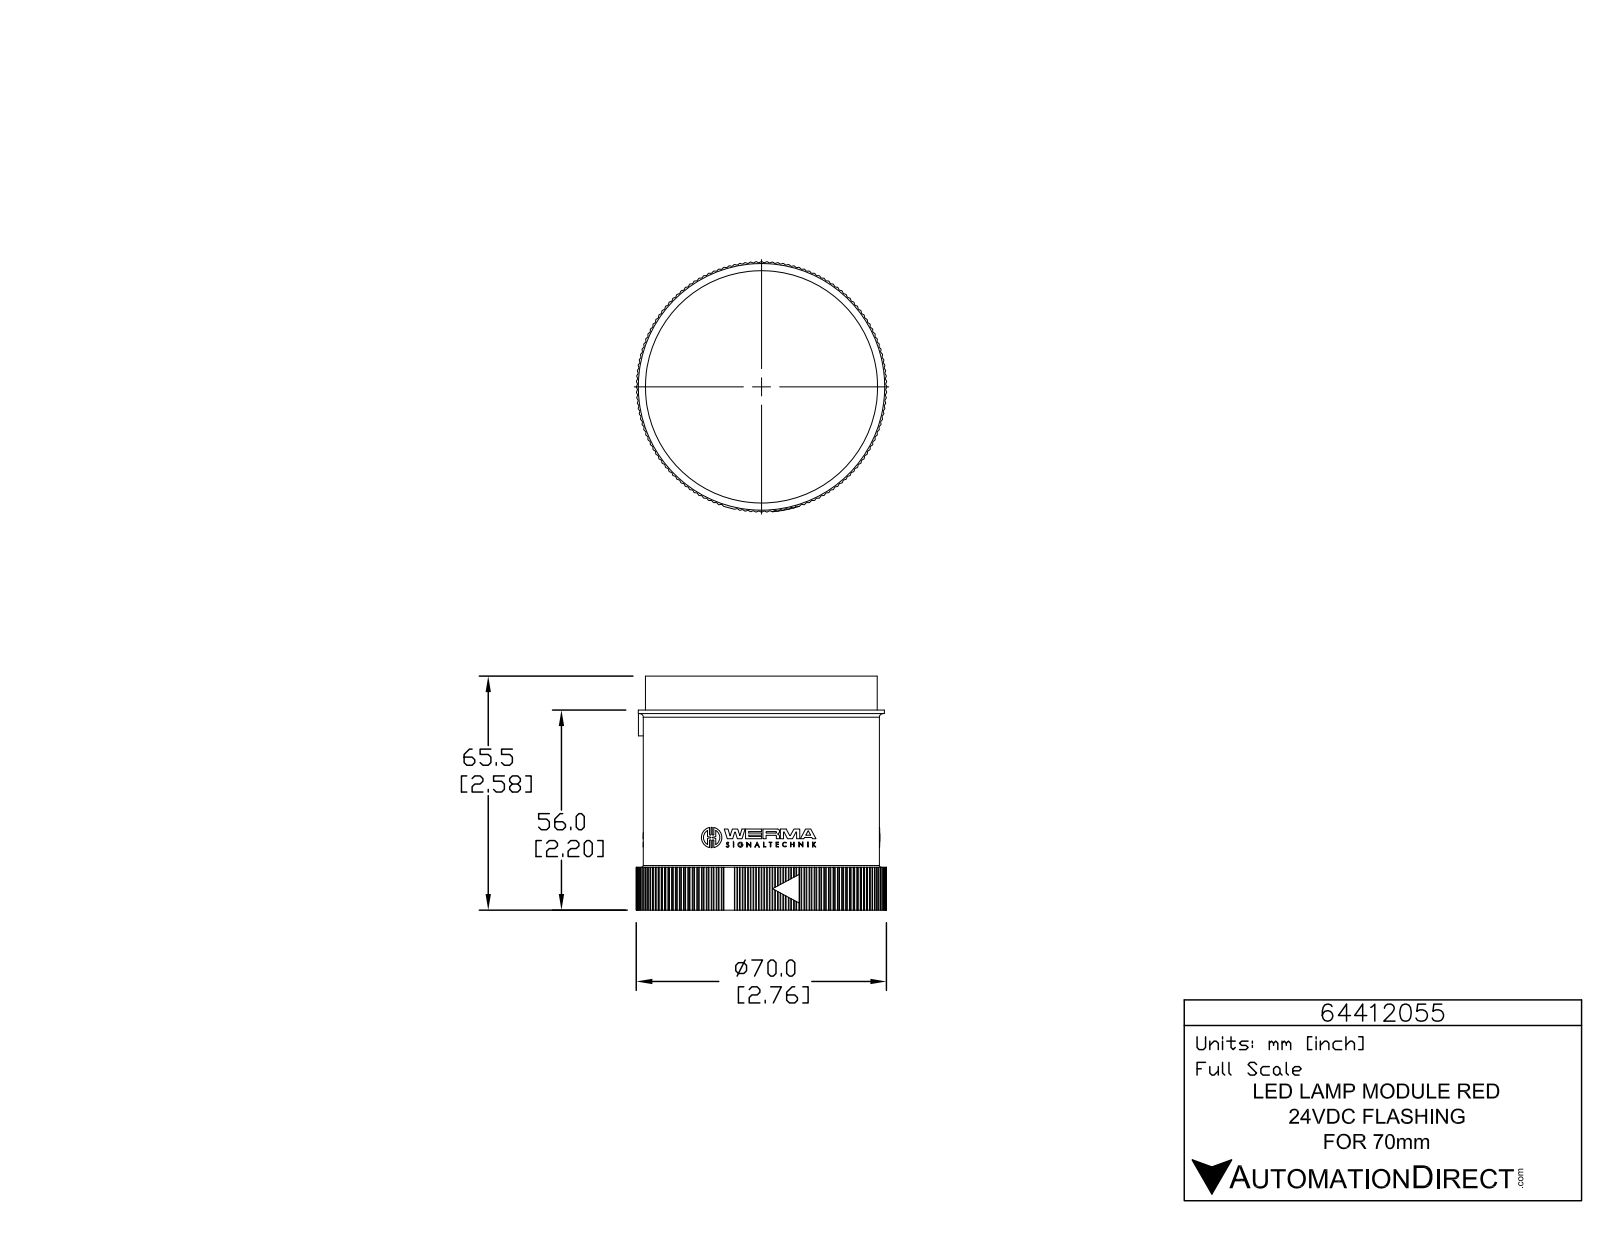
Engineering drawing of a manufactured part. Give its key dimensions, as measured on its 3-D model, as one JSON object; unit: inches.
{"part_name": "64412055", "step_written_by": "SolidWorks 2015 (AUTOMOTIVE_DESIGN)", "units": "inches", "bodies": {"solids": 1, "faces": 1400, "planar": 832, "cylindrical": 563, "other": 5}, "overall_size": [2.762, 2.762, 2.579], "volume_in3": 12.02, "surface_area_in2": 37.48, "round_holes": [[0.039, 3], [2.575, 1]], "round_bosses_or_shafts": [[0.226, 3], [0.056, 3], [2.717, 1], [2.606, 1], [2.559, 1]], "partial_cylinders_radius": [[0.008, 285], [0.008, 6], [0.008, 6], [0.008, 6], [0.131, 6], [0.004, 3], [0.005, 3], [0.008, 3]], "face_to_face_distances": [2.201, 2.451, 0.378, 2.579, 2.205, 1.827, 0.374, 2.452, 0.472, 0.094]}
